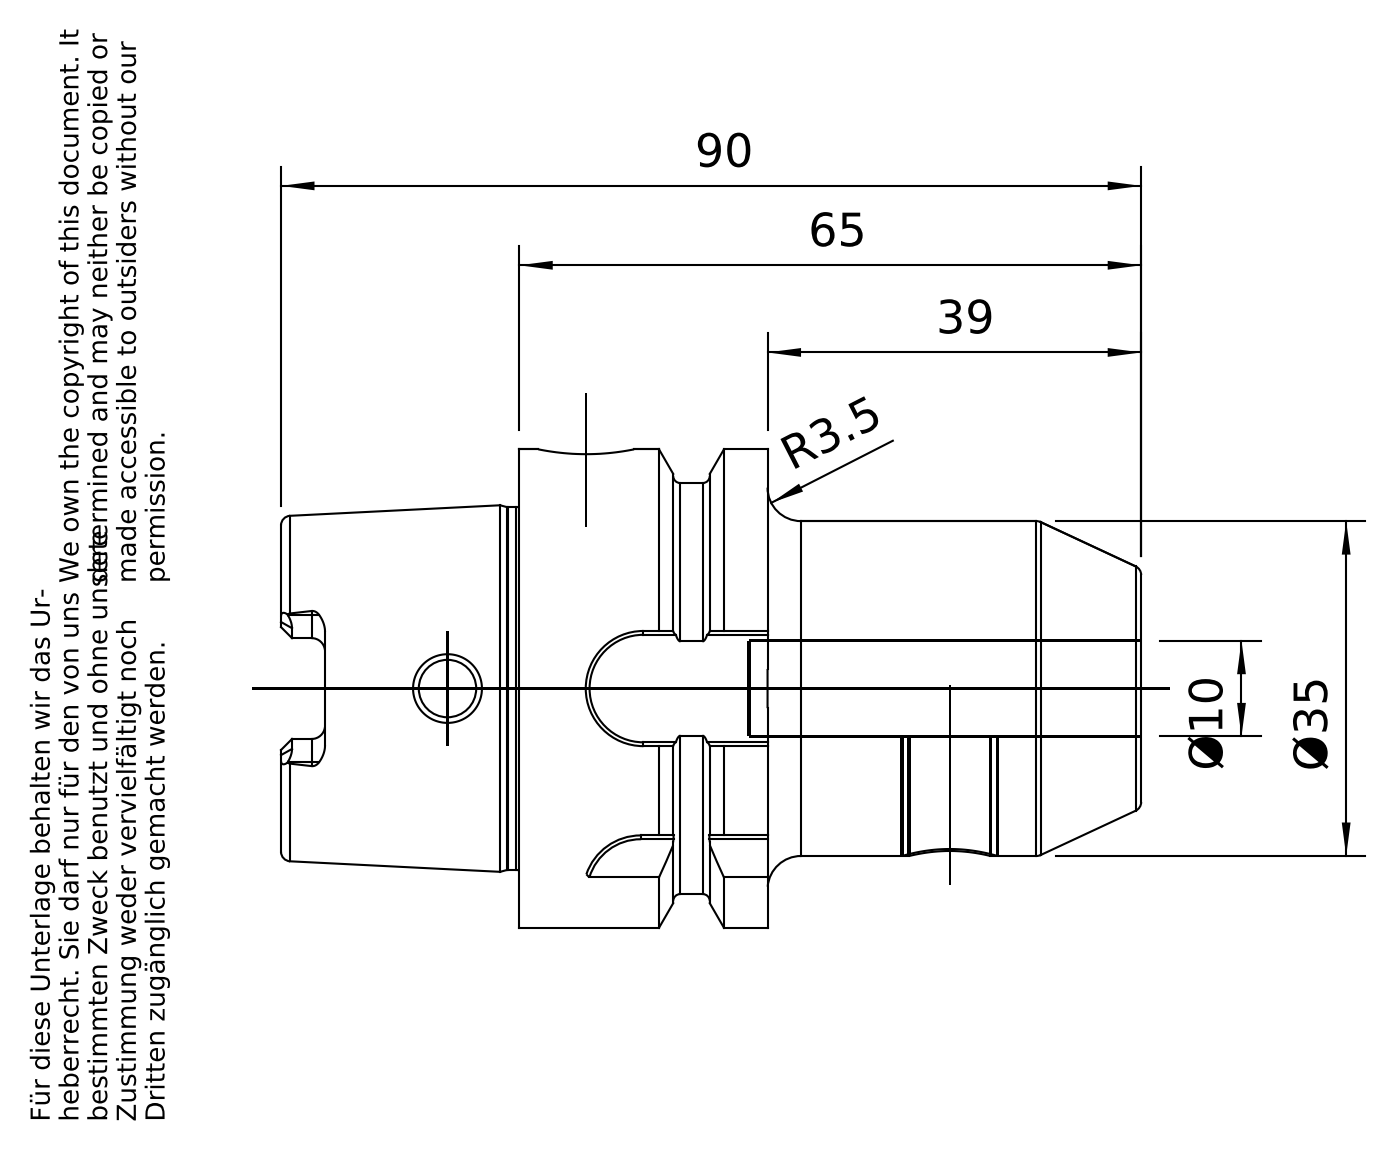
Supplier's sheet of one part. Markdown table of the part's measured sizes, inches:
| quantity | value |
| --- | --- |
| part name | A50-000-10 |
| STEP written by | PRO/ENGINEER BY PARAMETRIC TECHNOLOGY CORPORATION, 2010430 (CONFIG_CONTROL_DESIGN) |
| units | inches |
| bodies | 1 solid, 191 faces (64 planar, 53 cylindrical, 74 other) |
| overall size | 3.539 × 1.969 × 1.969 |
| volume | 4.889 in³ |
| surface area | 32.33 in² |
| round holes (diameter × count) | 0.394 × 3, 0.236 × 1, 0.335 × 1, 0.551 × 1, 0.63 × 1, 0.643 × 1, 0.65 × 1, 1.025 × 1, 1.263 × 1 |
| round bosses / shafts (diameter × count) | 1.969 × 1, 1.691 × 1, 1.493 × 1, 1.378 × 1 |
| partial cylindrical surfaces (radius × count) | 0.055 × 6, 0.094 × 4, 0.236 × 3, 0.237 × 1 |
| main face-to-face distances | 1.022, 2.559, 1.537, 0.98, 2.002, 3.539, 1.372, 0.392, 0.63, 2.167 |
| hole center spacings | 1.496 |
